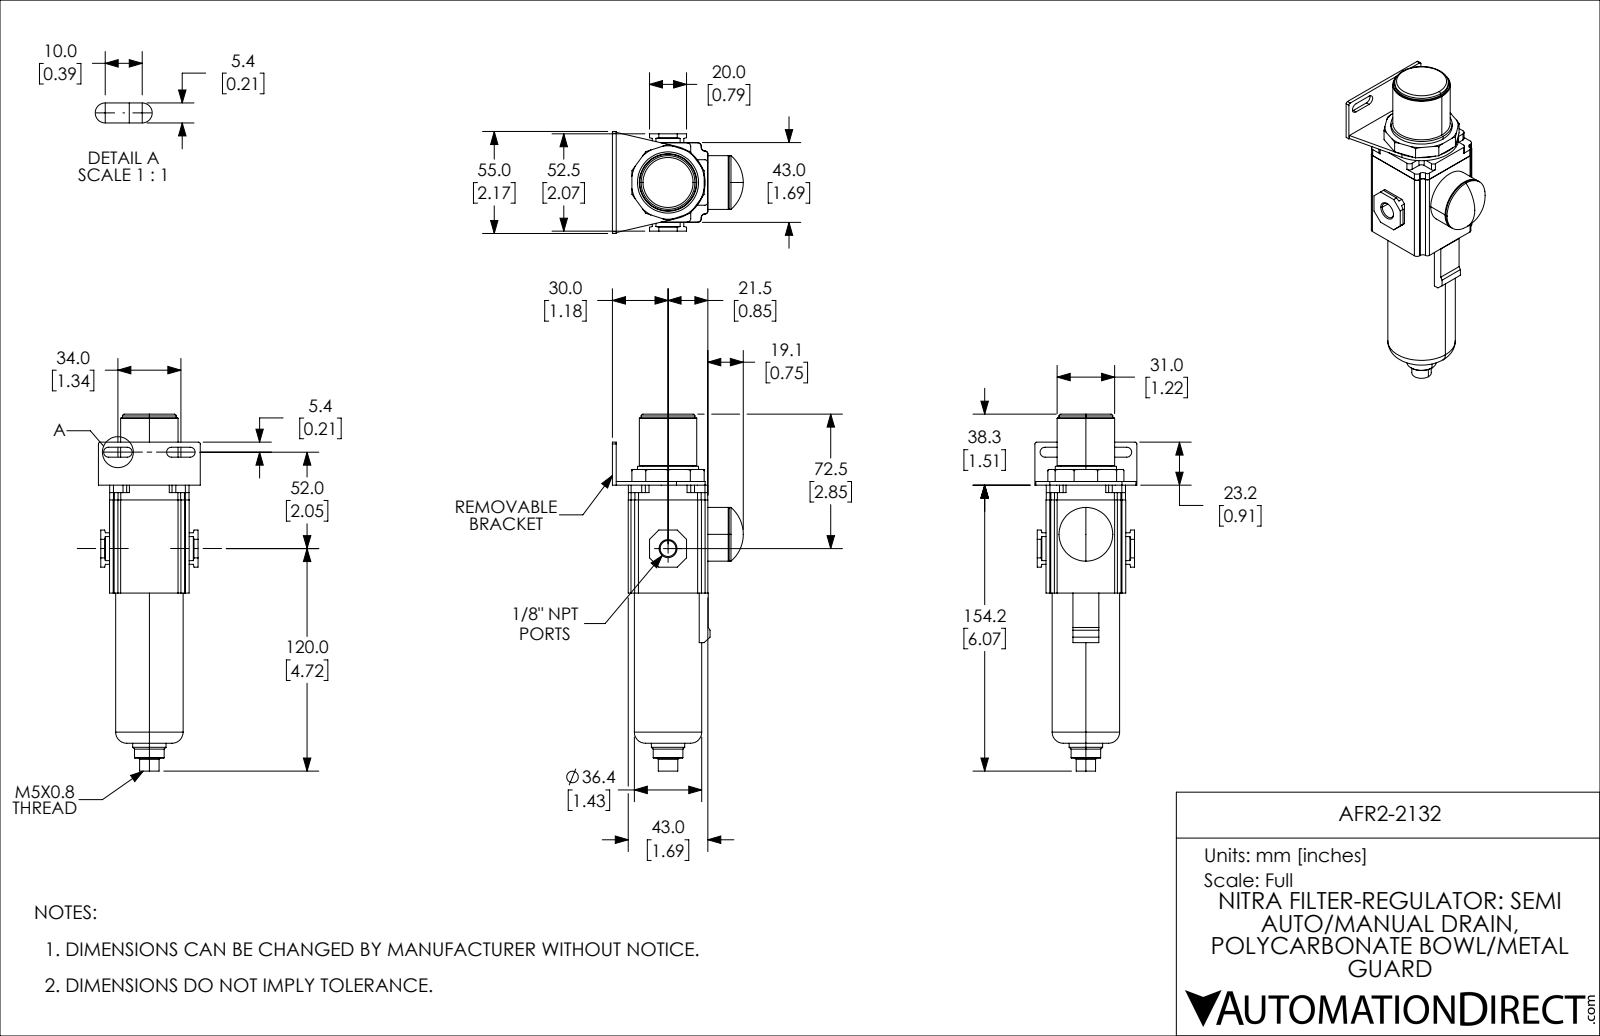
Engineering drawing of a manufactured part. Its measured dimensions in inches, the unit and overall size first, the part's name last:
Units: inches
Overall size (bounding box): 7.579 × 2.78 × 2.165
Round holes (diameter × count): ⌀0.163 ×1, ⌀0.337 ×1
Round bosses / shafts (diameter × count): ⌀1.142 ×2, ⌀1.433 ×1, ⌀1.299 ×1, ⌀1.22 ×1, ⌀1.054 ×1, ⌀0.709 ×1, ⌀0.63 ×1, ⌀0.413 ×1
Partial cylindrical surfaces — rounded edges, fillets, slot ends (radius × count): R0.079 ×24, R0.059 ×12, R0.106 ×4, R0.039 ×2, R0.787 ×1
Main face-to-face distances: 1.693, 0.079, 0.335, 0.256, 1.949, 2.028, 1.689, 1.429, 2.291, 2.37
Volume: 14.58 in³ · Surface area: 52.23 in²
Bodies: 1 solid, 220 faces (119 planar, 69 cylindrical, 32 other)
Part name (STEP PRODUCT): AFR2-2132
STEP written by: SolidWorks 2019 (CONFIG_CONTROL_DESIGN)
